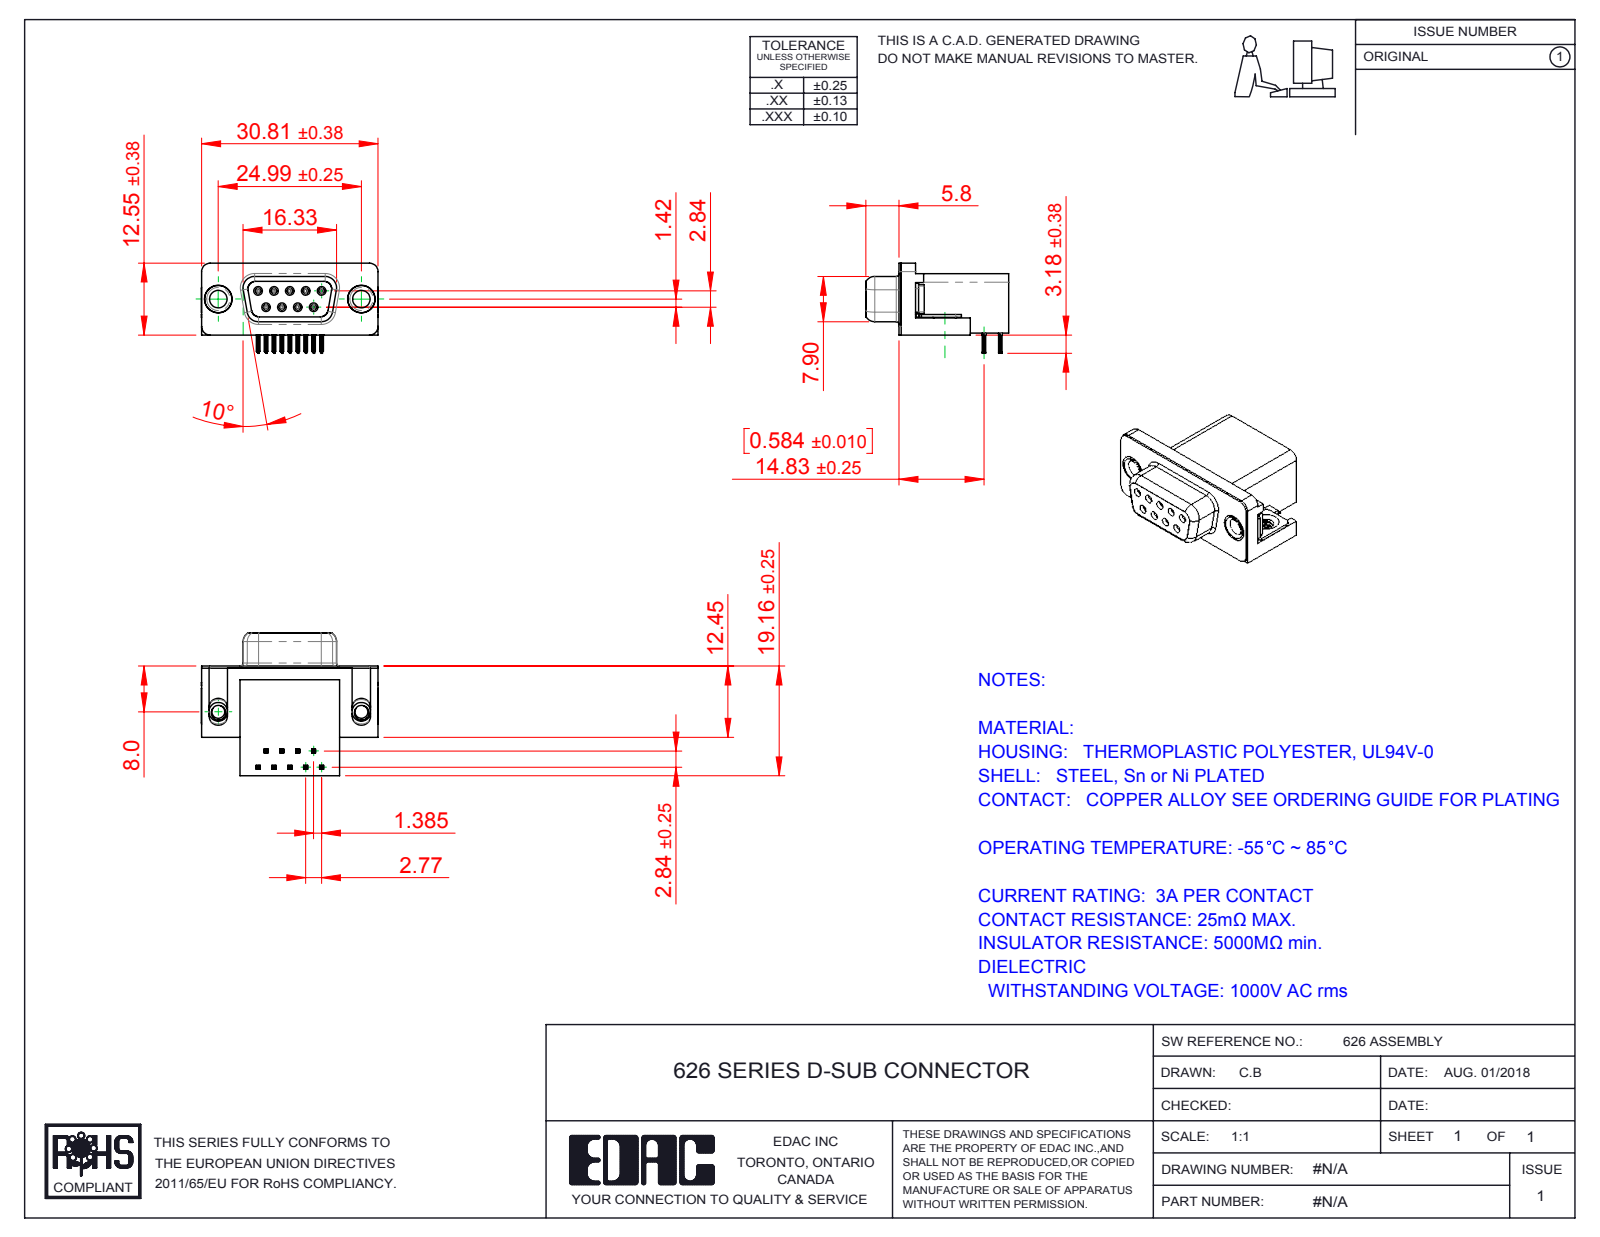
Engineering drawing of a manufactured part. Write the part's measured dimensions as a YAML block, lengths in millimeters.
part_name: "626 4-40 Threaded Board Mount; 626 Contact Bottom; 626 Thru Hole Rivet; 626 Shell_9 Socket (+3 more)"
step_written_by: "SolidWorks 2016 (CONFIG_CONTROL_DESIGN)"
units: millimeters
bodies: {solids: 15, faces: 1564, planar: 686, cylindrical: 410, other: 468}
overall_size: [30.89, 24.96, 15.73]
volume: 4967
surface_area: 5847
round_holes:
  - {diameter: 0.8, count: 9}
  - {diameter: 0.9, count: 9}
  - {diameter: 2.26, count: 2}
  - {diameter: 3.05, count: 2}
  - {diameter: 4, count: 2}
  - {diameter: 4.8, count: 2}
  - {diameter: 5, count: 2}
round_bosses_or_shafts:
  - {diameter: 1.2, count: 9}
  - {diameter: 4.9, count: 2}
  - {diameter: 4.75, count: 2}
  - {diameter: 3.85, count: 2}
  - {diameter: 3.26, count: 2}
partial_cylinders:
  - {radius: 0.1, count: 72}
  - {radius: 0.15, count: 36}
  - {radius: 0.35, count: 18}
  - {radius: 1, count: 18}
  - {radius: 0.34, count: 9}
  - {radius: 0.25, count: 8}
  - {radius: 1.35, count: 8}
  - {radius: 1.6, count: 8}
face_to_face_distances: [0.4, 10.34, 0.35, 18.76, 19.16, 2.9, 2.5, 6.2, 16.26, 10.69]
hole_center_spacings: [3.16, 2.77, 5.54, 5.03, 5.04, 8.31, 7.48, 7.49]
